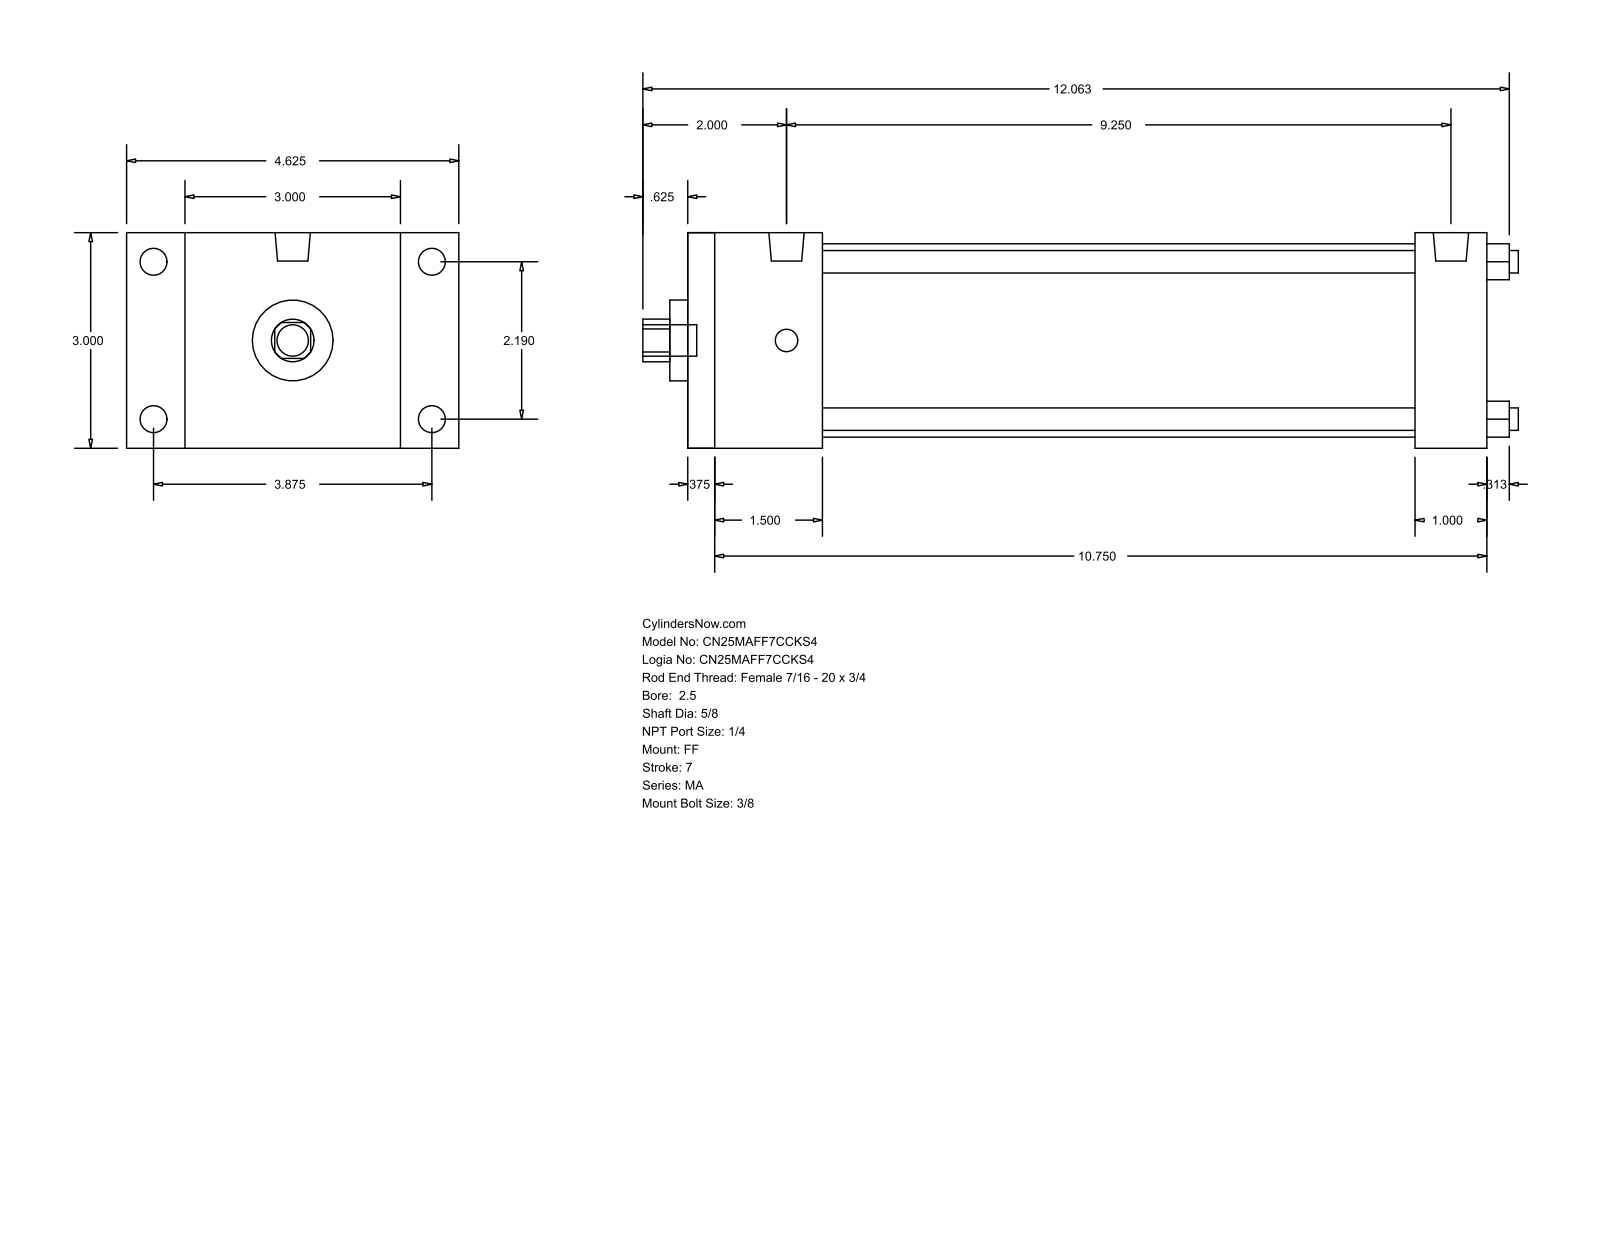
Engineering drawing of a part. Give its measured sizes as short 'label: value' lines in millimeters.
name: MA_FF__0250_0.625
written by: GSSL Pune (CONFIG_CONTROL_DESIGN)
unit: mm
bodies: 0 solids, 92 faces (64 planar, 28 cylindrical, 0 other)
size: 309.56 × 117.47 × 76.2
holes: 4× ⌀7.94, 1× ⌀15.88, 1× ⌀28.57, 1× ⌀68.33
bosses: 4× ⌀9.53, 4× ⌀7.94, 2× ⌀12.49, 1× ⌀11.11
rounds: 1× R7.54
face distances: 76.2, 282.57, 9.52, 273.05, 25.4, 47.62, 257.17, 38.1, 247.65, 209.55
hole spacings: 39.33, 55.62, 78.66
